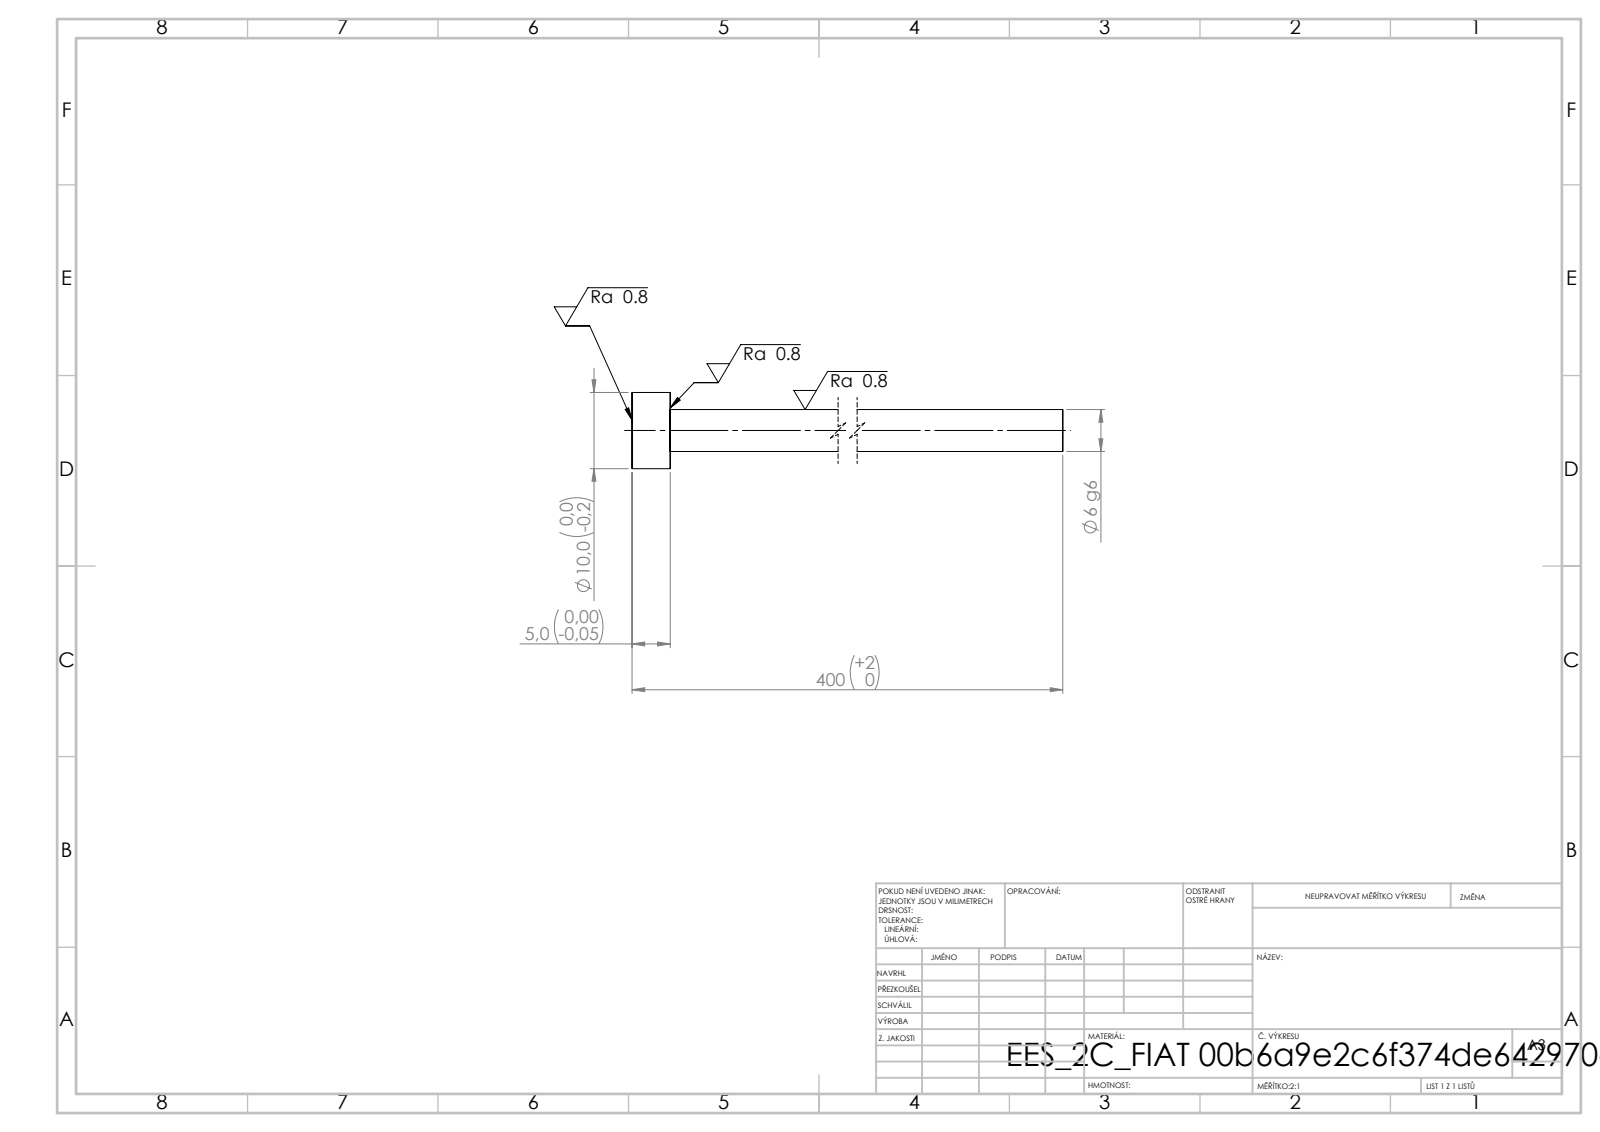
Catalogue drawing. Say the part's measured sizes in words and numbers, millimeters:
Its 3-D file was written by "SolidWorks 2019 (CONFIG_CONTROL_DESIGN)". It is 1 solid with 7 faces: 3 planar, 4 cylindrical and 0 other. Overall it measures 400 by 10 by 10 millimeters. Its volume is 9 777 cubic millimeters and its surface area 7 139 square millimeters. Round bosses or shafts: 1 of diameter 10, 1 of diameter 5.5. The main face-to-face distances are 5, 400, 395.
